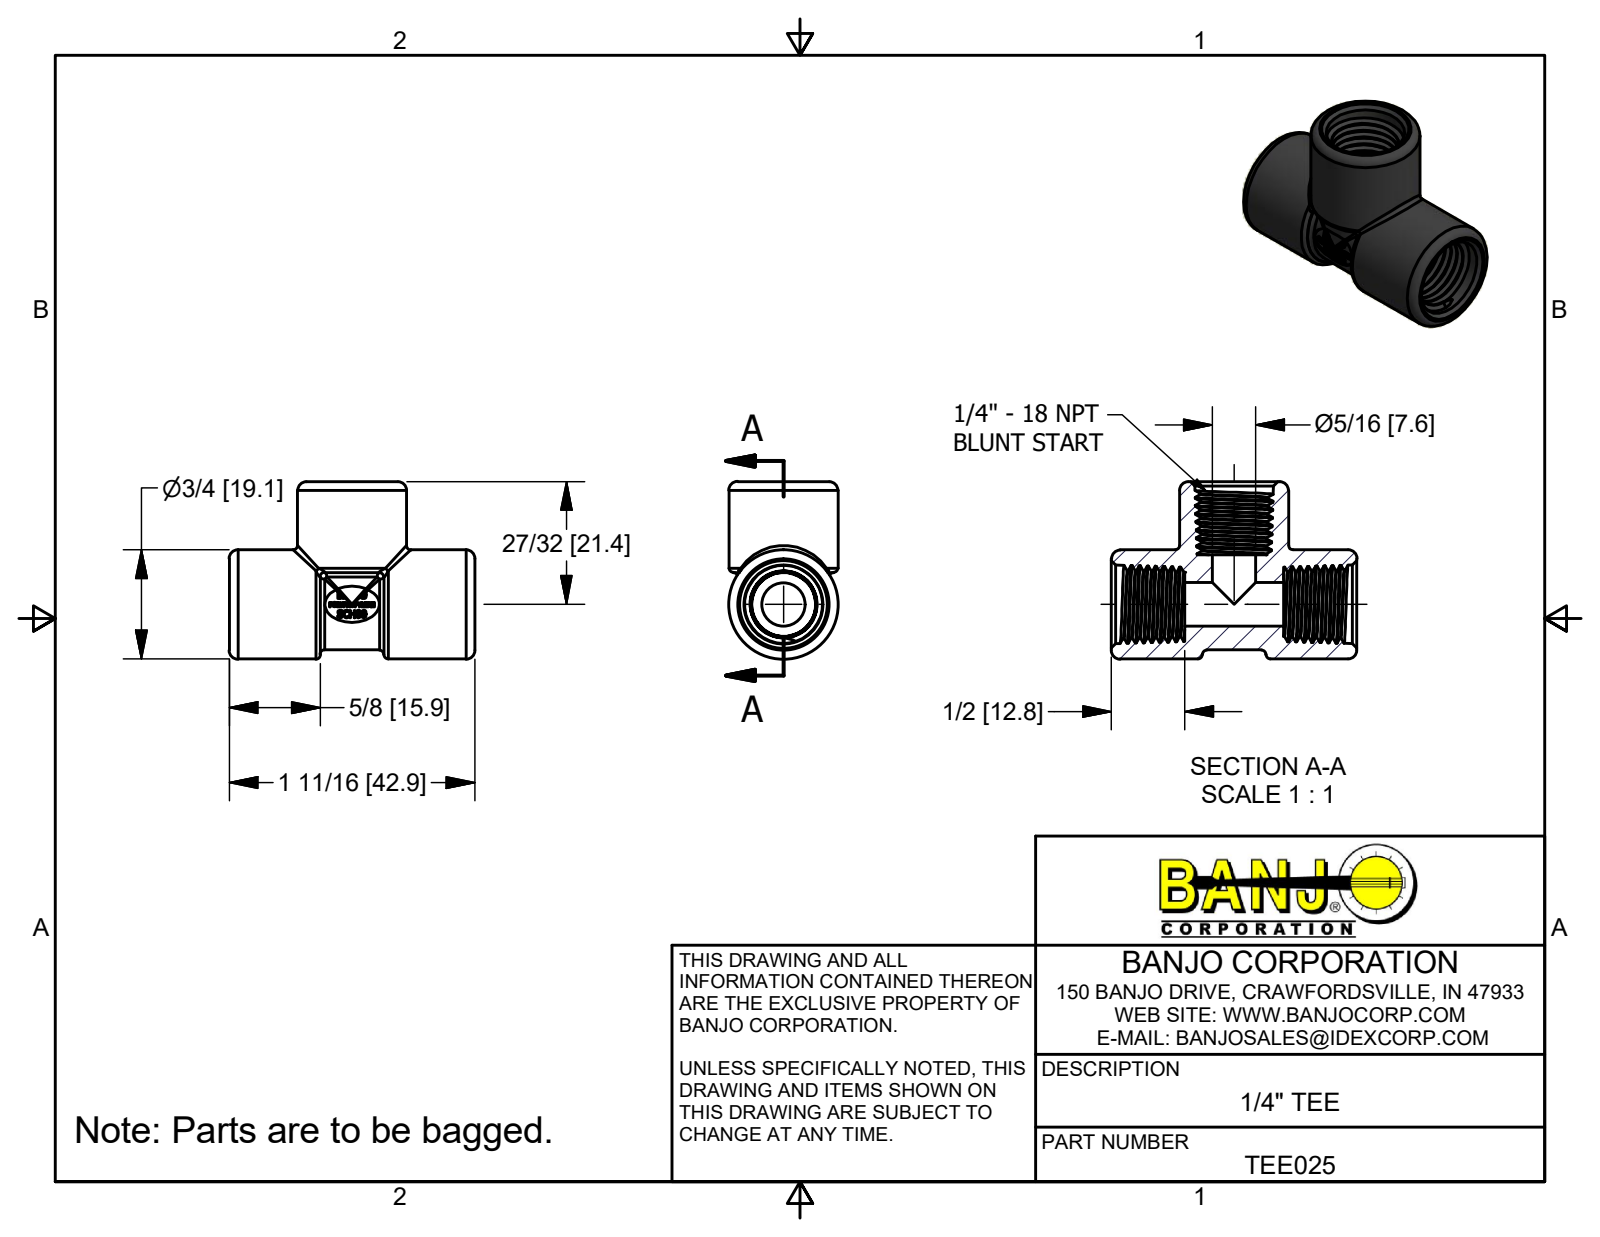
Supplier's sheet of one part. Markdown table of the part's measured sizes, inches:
| quantity | value |
| --- | --- |
| part name | TEE025; TEE025U |
| STEP written by | Autodesk Inventor 2018 (AUTOMOTIVE_DESIGN) |
| units | inches |
| bodies | 1 solid, 409 faces (141 planar, 50 cylindrical, 218 other) |
| overall size | 8.718 × 8.718 × 0.75 |
| volume | 0.571 in³ |
| surface area | 36.94 in² |
| round holes (diameter × count) | 0.298 × 2 |
| round bosses / shafts (diameter × count) | 0.75 × 2 |
| partial cylindrical surfaces (radius × count) | 0.171 × 3, 0.03 × 2, 0.302 × 2, 0.313 × 2 |
| main face-to-face distances | 0.68, 0.504, 1.183, 1.687, 0.625, 0.121, 1.063, 0.559, 0.438, 0.118 |
